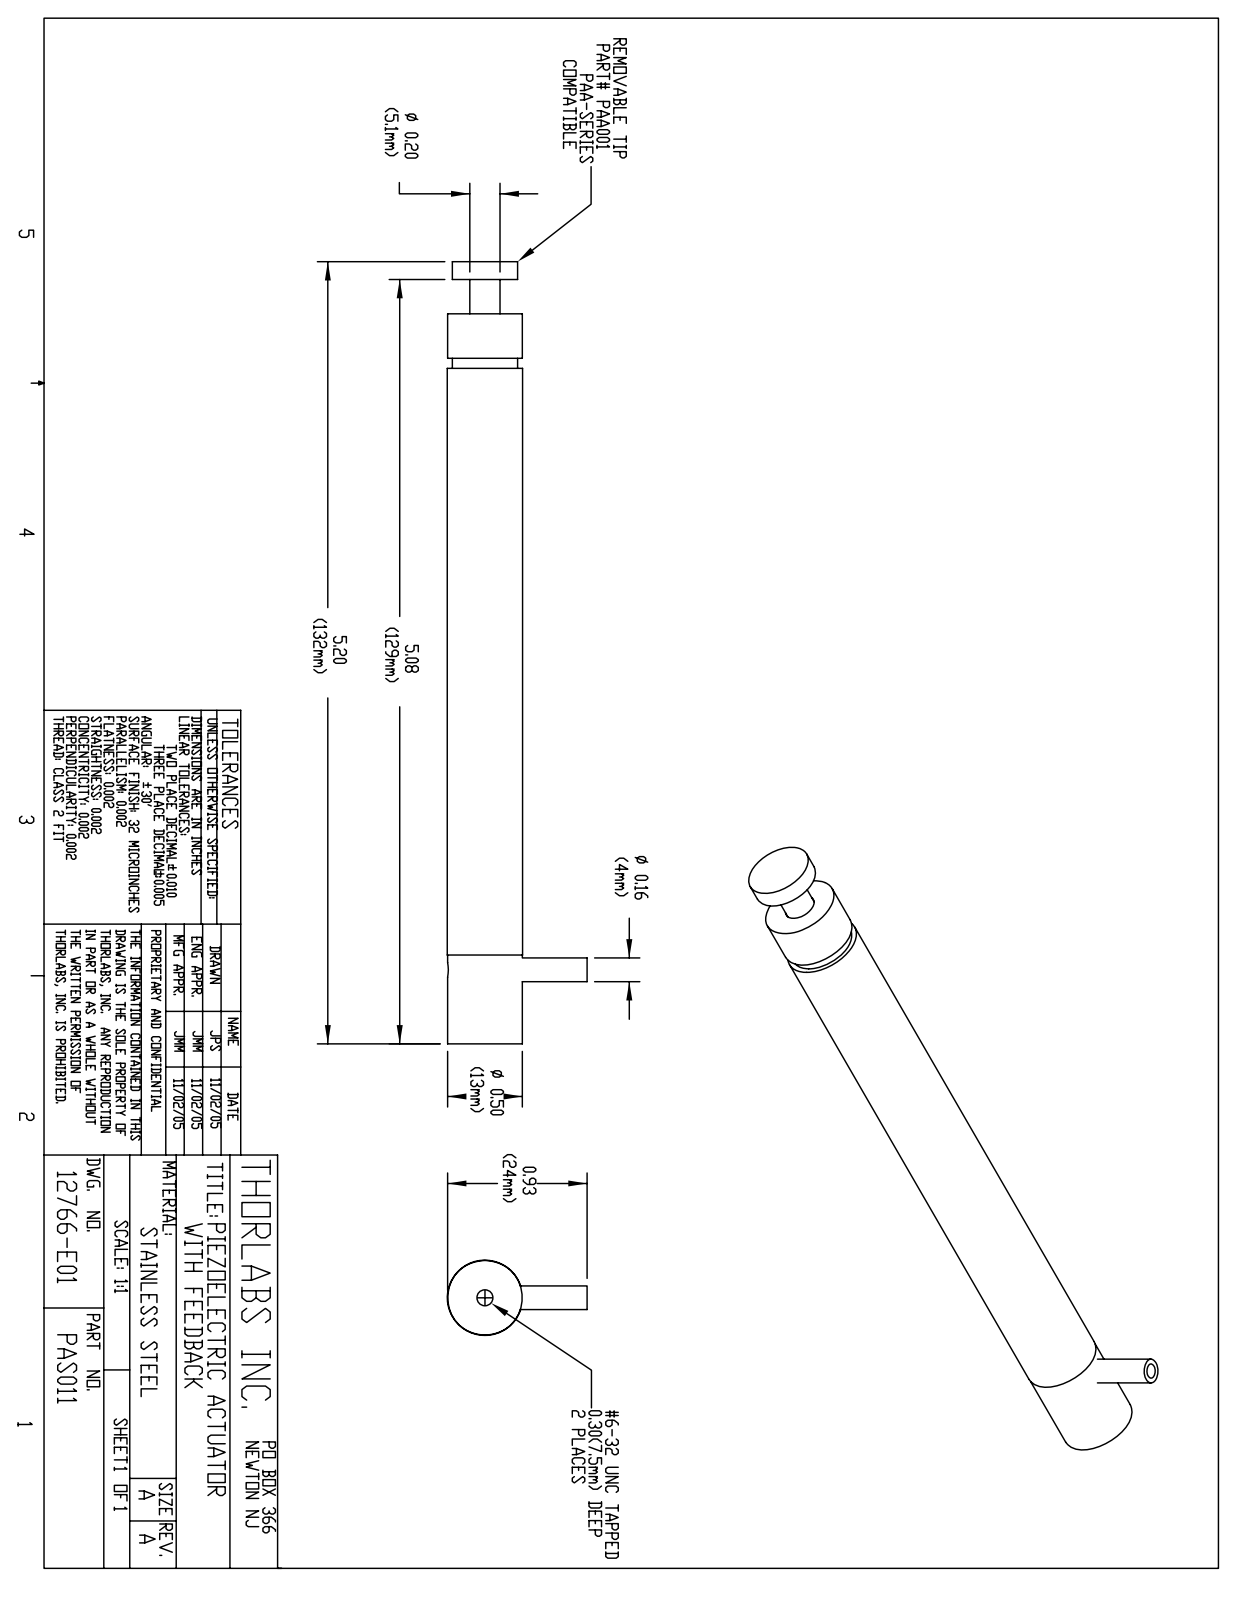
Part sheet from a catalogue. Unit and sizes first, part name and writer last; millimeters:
Units: millimetres
Overall size (bounding box): 132 × 23.6 × 12.7
Round holes (diameter × count): ⌀2.5 ×2, ⌀2.4 ×1, ⌀2.7 ×1, ⌀5.3 ×1, ⌀9.3 ×1, ⌀9.6 ×1, ⌀11.4 ×1
Round bosses / shafts (diameter × count): ⌀12.7 ×1, ⌀12.6 ×1, ⌀11 ×1, ⌀5.1 ×1, ⌀4 ×1
Main face-to-face distances: 123.2, 8.8, 132, 3, 5.8, 129, 15, 114, 122, 119
Bodies: 0 solids, 41 faces (11 planar, 30 cylindrical, 0 other)
Part name (STEP PRODUCT): 12766-E0W
STEP written by: SolidWorks 2007 (AUTOMOTIVE_DESIGN)
